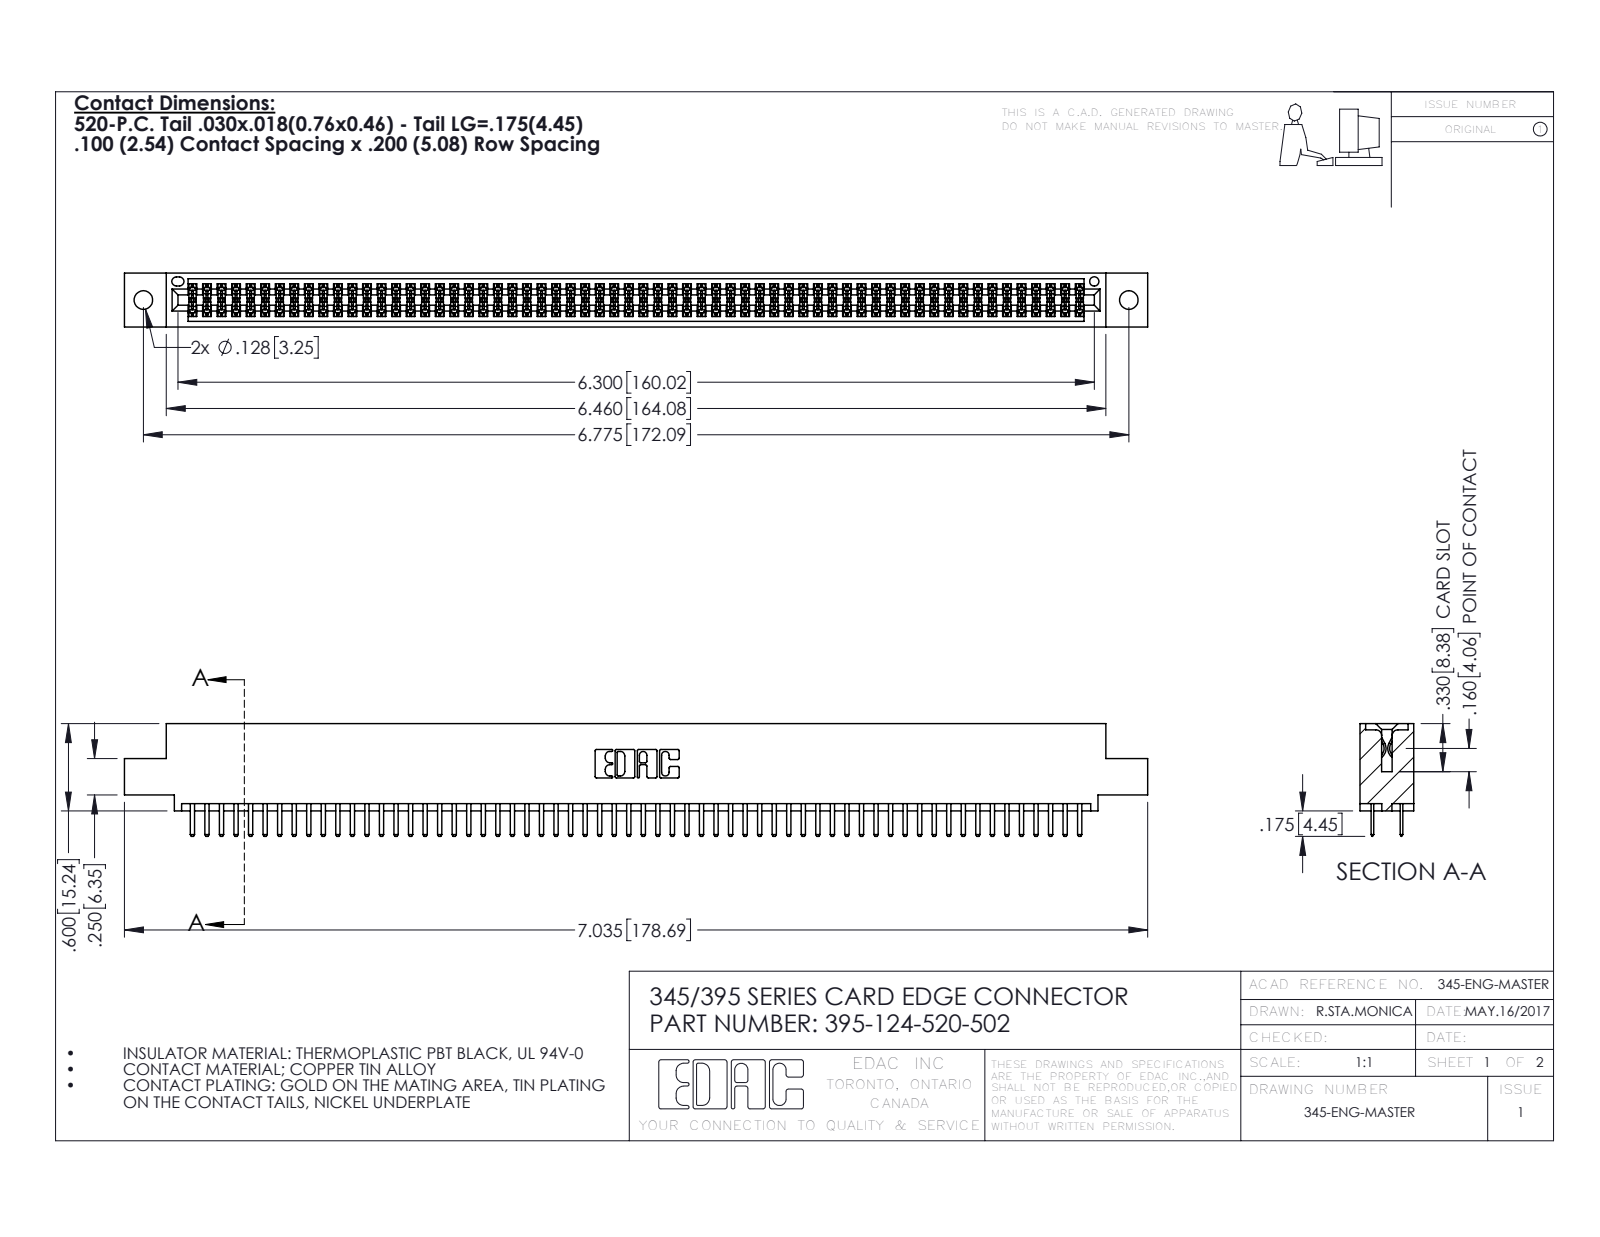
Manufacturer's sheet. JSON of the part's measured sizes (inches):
{"part_name": "345 Part_0.110 Offset - 0.128 Dia; 395-124-520-502; 345-292-001_345-293-120", "step_written_by": "SolidWorks 2016 (CONFIG_CONTROL_DESIGN)", "units": "inches", "bodies": {"solids": 125, "faces": 6826, "planar": 4424, "cylindrical": 2402, "other": 0}, "overall_size": [7.035, 0.775, 0.37], "volume_in3": 1.061, "surface_area_in2": 39.96, "round_holes": [[0.128, 2], [0.064, 1]], "partial_cylinders_radius": [[0.006, 186], [0.01, 128], [0.01, 22], [0.007, 6], [0.031, 6], [0.026, 3], [0.014, 2], [0.019, 2]], "face_to_face_distances": [0.298, 0.072, 0.2, 0.37, 0.098, 0.272, 0.025, 0.225, 0.022, 0.072], "hole_center_spacings": [0.27, 6.539, 6.775]}
